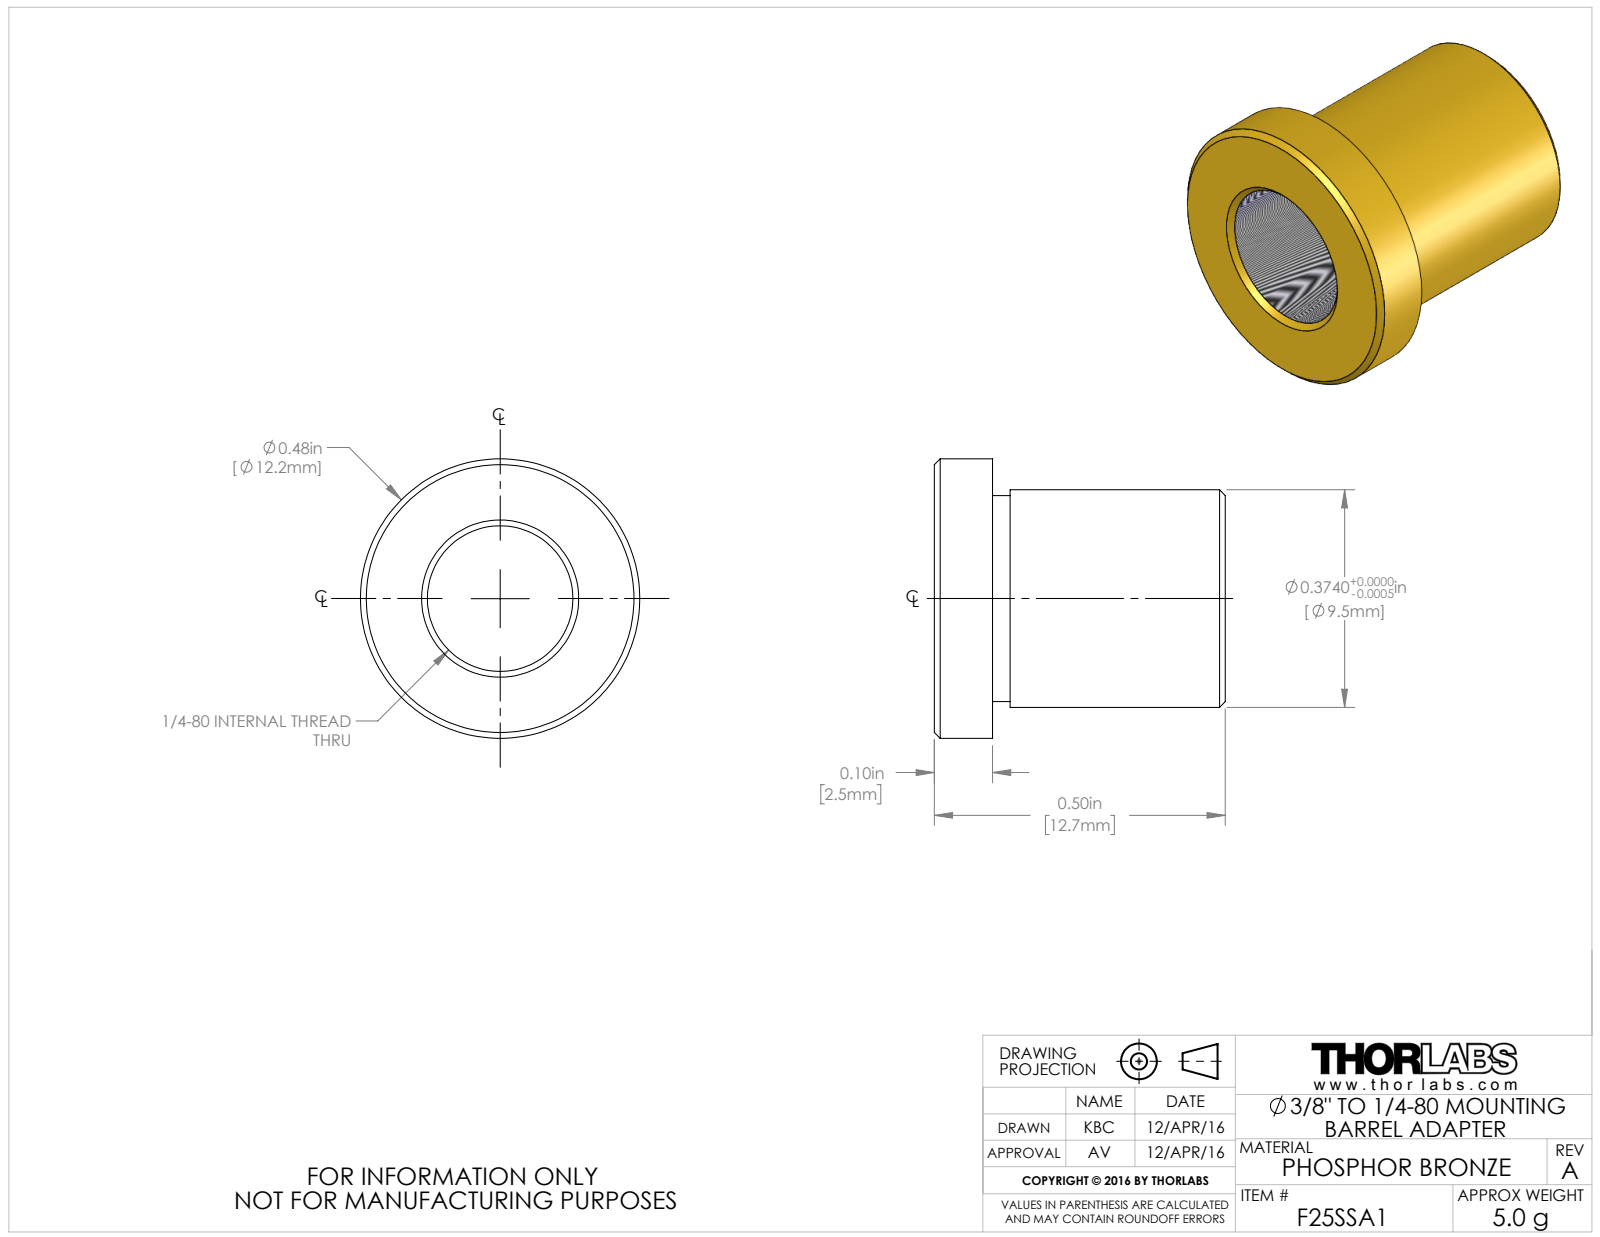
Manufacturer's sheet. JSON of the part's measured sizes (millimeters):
{"part_name": "TTN099737-E0W", "step_written_by": "SolidWorks 2014 (CONFIG_CONTROL_DESIGN)", "units": "millimeters", "bodies": {"solids": 1, "faces": 20, "planar": 4, "cylindrical": 8, "other": 8}, "overall_size": [12.7, 12.2, 12.2], "volume_mm3": 610, "surface_area_mm2": 821, "round_holes": [[6.4, 1]], "round_bosses_or_shafts": [[12.2, 1], [9.5, 1], [9, 1]], "face_to_face_distances": [2.5, 10.2, 12.7, 9.4, 0.8, 3.3]}
